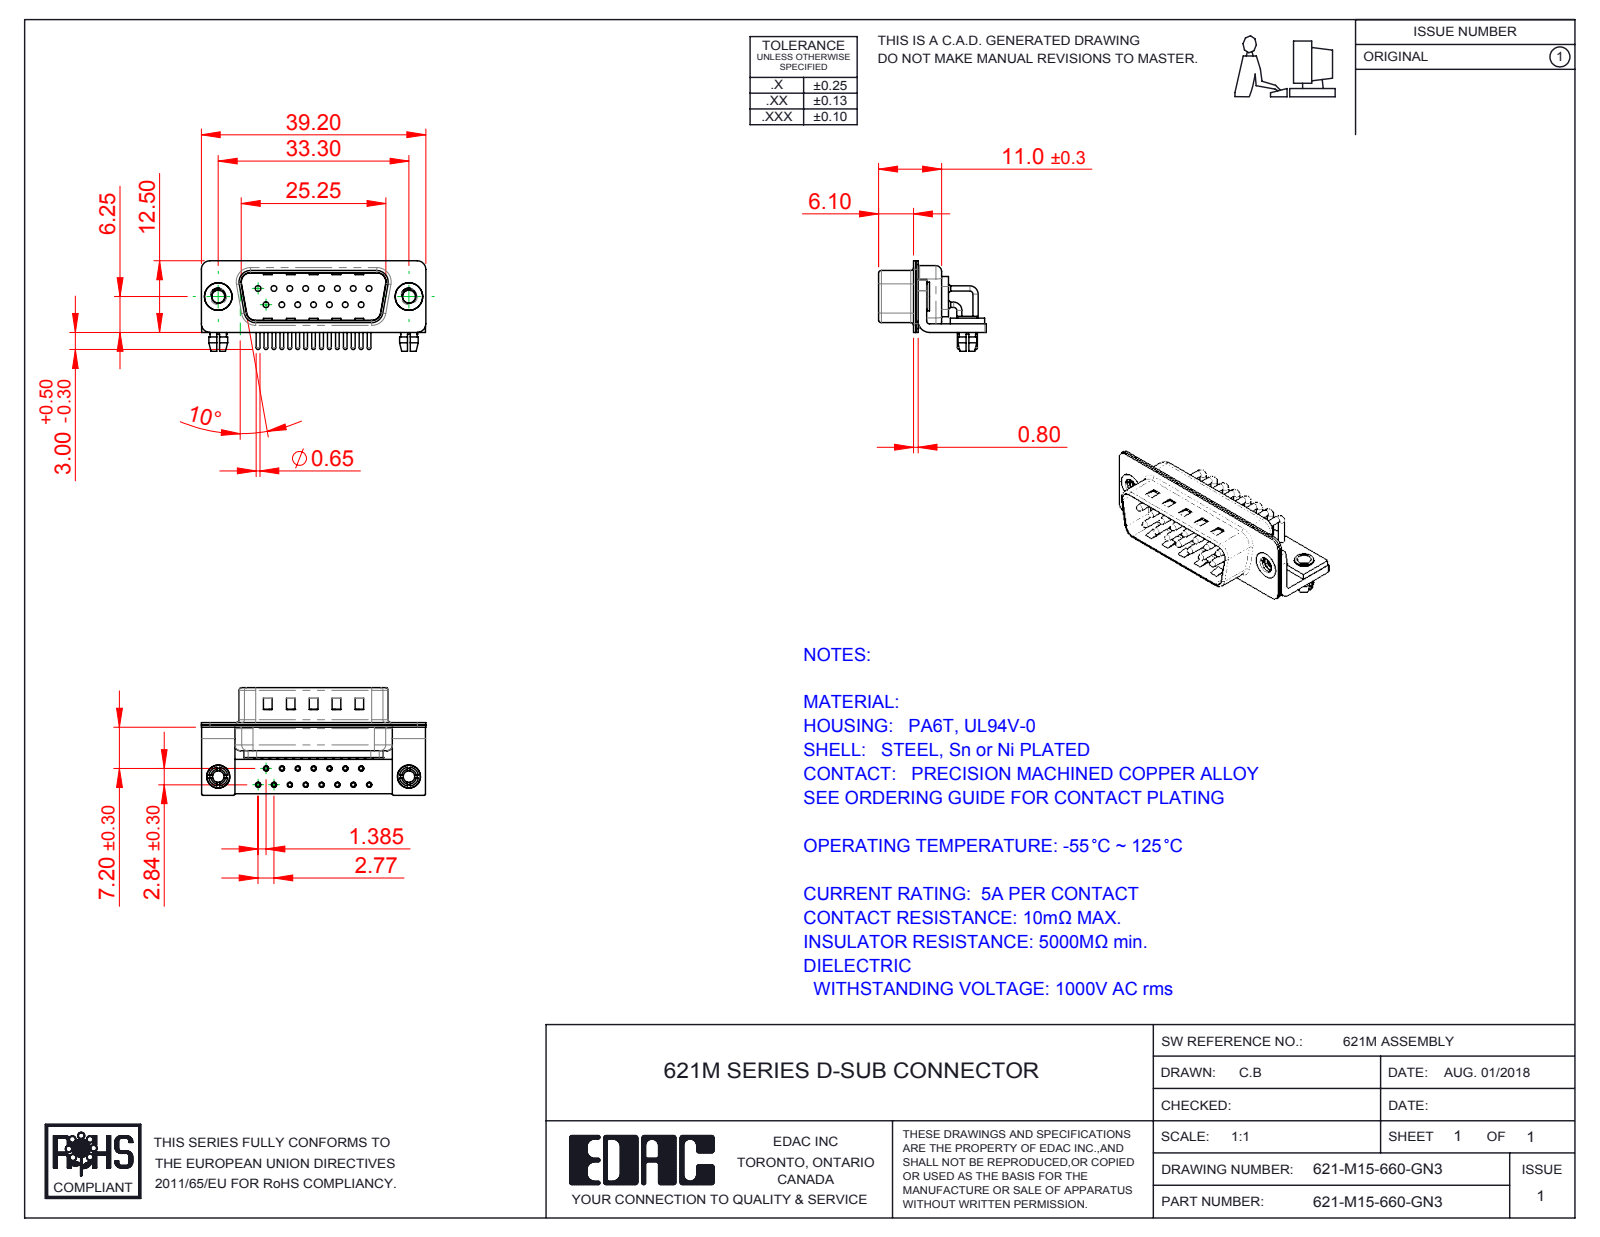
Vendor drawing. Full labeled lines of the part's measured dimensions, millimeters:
Part name (STEP PRODUCT): 621M Stabilizer Board_15 Contacts; 621M Housing_15 Contacts; 621M Shell Rear_15 Contacts; 621-M15-660-GN3 (+6 more)
STEP written by: SolidWorks 2016 (CONFIG_CONTROL_DESIGN)
Units: millimetres
Bodies: 25 solids, 2162 faces (1173 planar, 757 cylindrical, 232 other)
Overall size (bounding box): 39.2 × 18.8 × 15.8
Volume: 2 417 mm³ · Surface area: 6 593 mm²
Round holes (diameter × count): ⌀2 ×17, ⌀0.9 ×15, ⌀1 ×15, ⌀1.7 ×15, ⌀2.26 ×2, ⌀2.5 ×2, ⌀3.2 ×2, ⌀4 ×2, ⌀4.8 ×2
Round bosses / shafts (diameter × count): ⌀0.9 ×22, ⌀1.5 ×15, ⌀0.65 ×15, ⌀5 ×2, ⌀4.9 ×2, ⌀4 ×2, ⌀3.4 ×2, ⌀3.3 ×2
Partial cylindrical surfaces — rounded edges, fillets, slot ends (radius × count): R0.25 ×16, R1.5 ×16, R1.01 ×15, R2 ×13, R0.5 ×9, R1.6 ×8, R0.6 ×4, R0.65 ×4
Main face-to-face distances: 0.4, 0.85, 1.5, 0.8, 1.25, 10.4, 9.55, 1, 2.1, 1.9
Hole centre spacings: 3.16, 2.77, 5.54, 8.31, 11.08, 5.03, 5.04, 7.48
